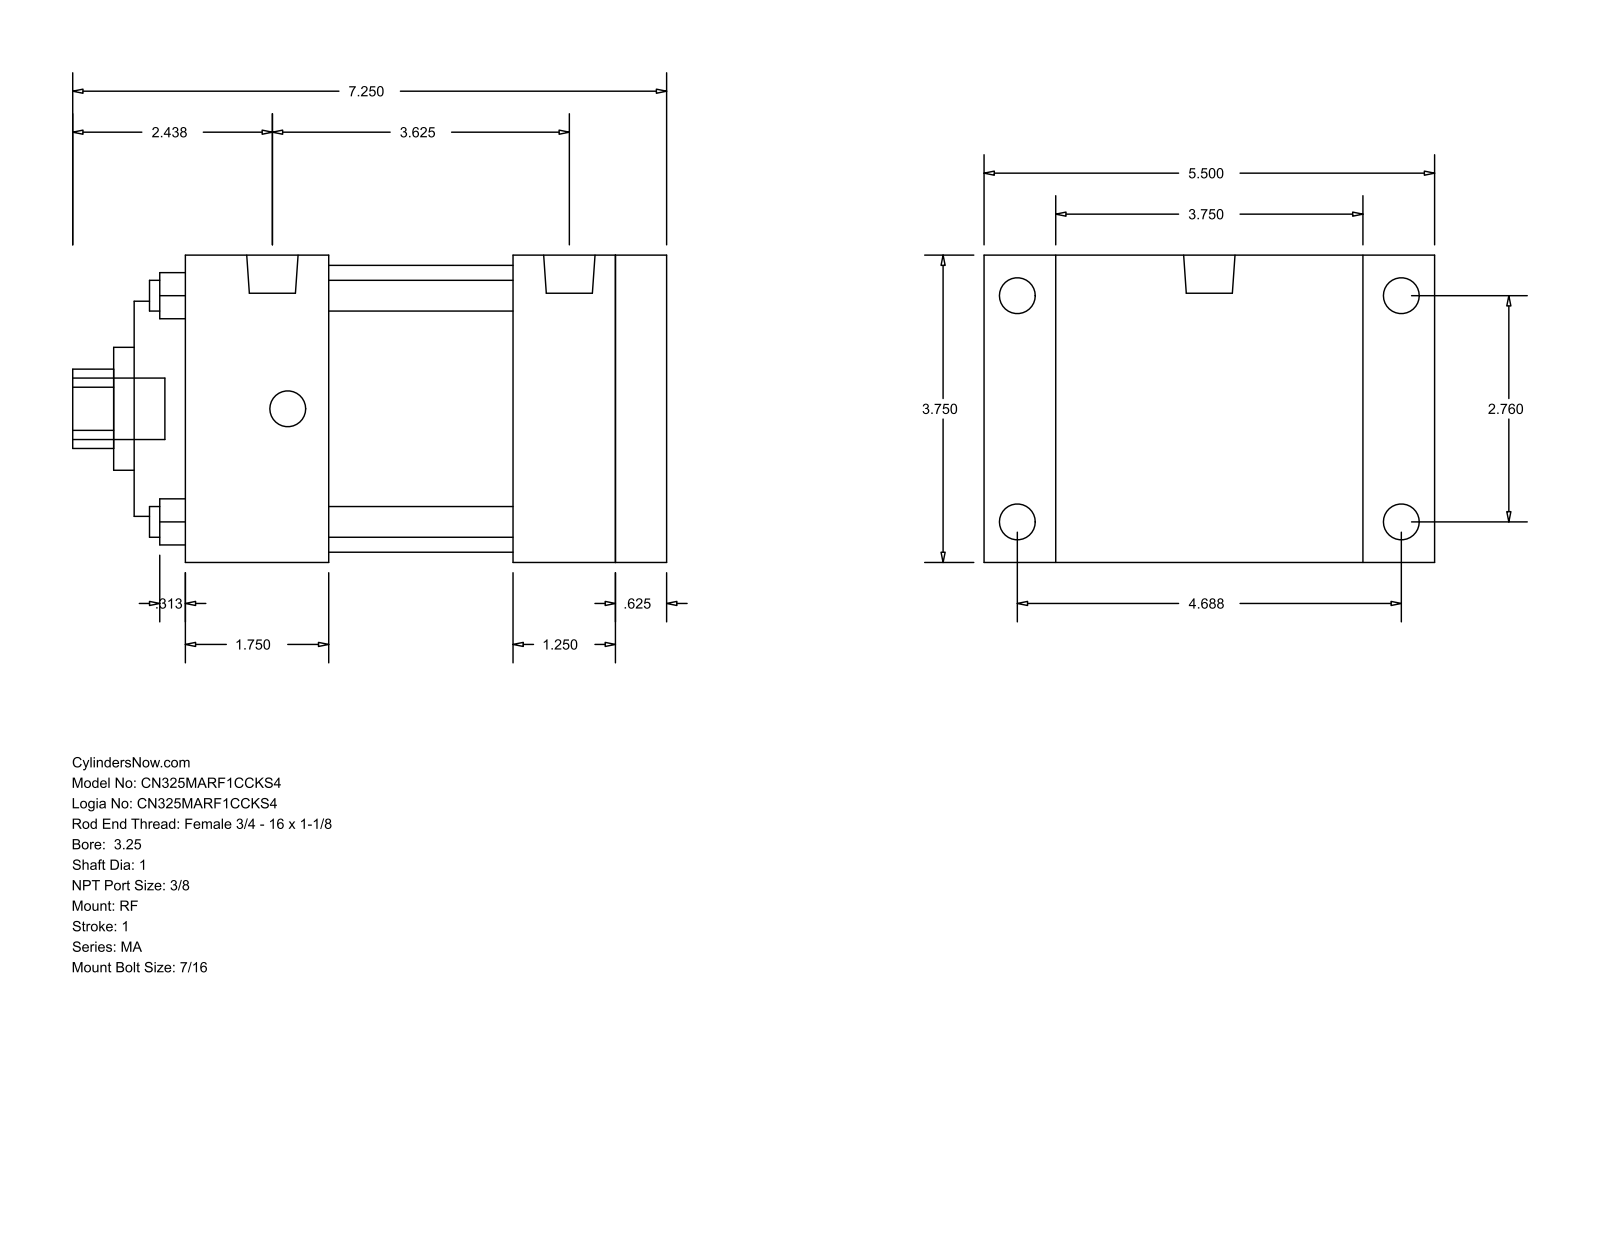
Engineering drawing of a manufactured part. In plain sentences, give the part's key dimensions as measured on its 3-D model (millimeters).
The part is named "MA_RF__0325_1". Its 3-D file was written by "GSSL Pune (CONFIG_CONTROL_DESIGN)". It is 0 solids with 94 faces: 65 planar, 29 cylindrical and 0 other. Overall it measures 184.15 by 139.7 by 95.25 millimeters. Round holes: 4 of diameter 9.53, 1 of diameter 25.4, 1 of diameter 38.1, 1 of diameter 66.67, 1 of diameter 88.9. Round bosses or shafts: 8 of diameter 11.11, 2 of diameter 15.93, 1 of diameter 19.05. Partial cylindrical surfaces (rounded edges, fillets, slot ends): 1 of radius 12.29. The main face-to-face distances are 95.24, 149.23, 15.87, 133.36, 22.23, 117.47, 101.61, 31.75, 47.62, 44.46. The hole center spacings are 49.57, 70.1, 99.14.
